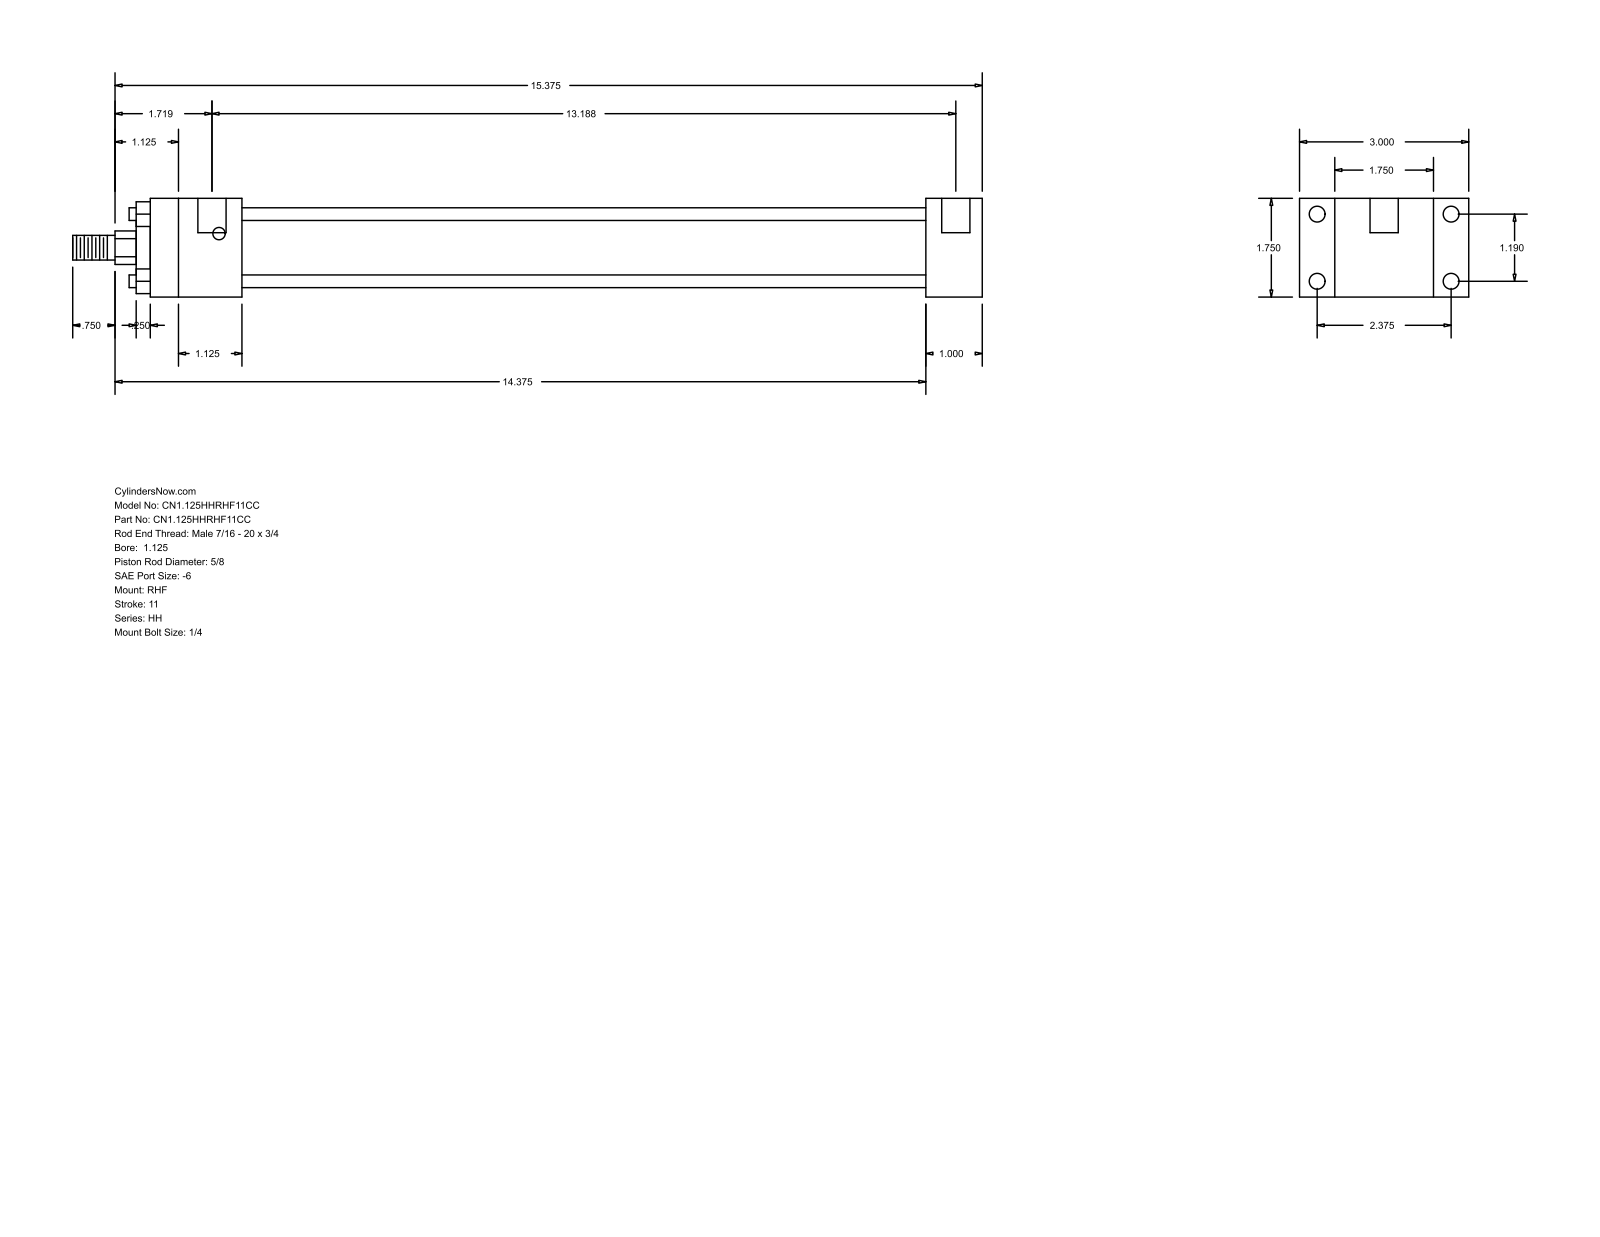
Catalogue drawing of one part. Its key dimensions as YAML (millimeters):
part_name: "HH_RHF__0112_0.625"
step_written_by: "GSSL Pune (CONFIG_CONTROL_DESIGN)"
units: millimeters
bodies: {solids: 0, faces: 88, planar: 60, cylindrical: 28, other: 0}
overall_size: [409.57, 76.2, 44.45]
round_holes:
  - {diameter: 5.56, count: 4}
  - {diameter: 7.14, count: 4}
  - {diameter: 12.7, count: 2}
round_bosses_or_shafts:
  - {diameter: 5.71, count: 4}
  - {diameter: 34.92, count: 1}
  - {diameter: 28.57, count: 1}
  - {diameter: 15.88, count: 1}
  - {diameter: 11.11, count: 1}
partial_cylinders:
  - {radius: 7.54, count: 1}
face_to_face_distances: [44.46, 15.87, 25.4, 60.33, 76.2, 307.97, 333.37, 41.27, 349.24, 374.64]
hole_center_spacings: [30.22, 60.32, 67.47, 331.79, 3.17, 334.96]
